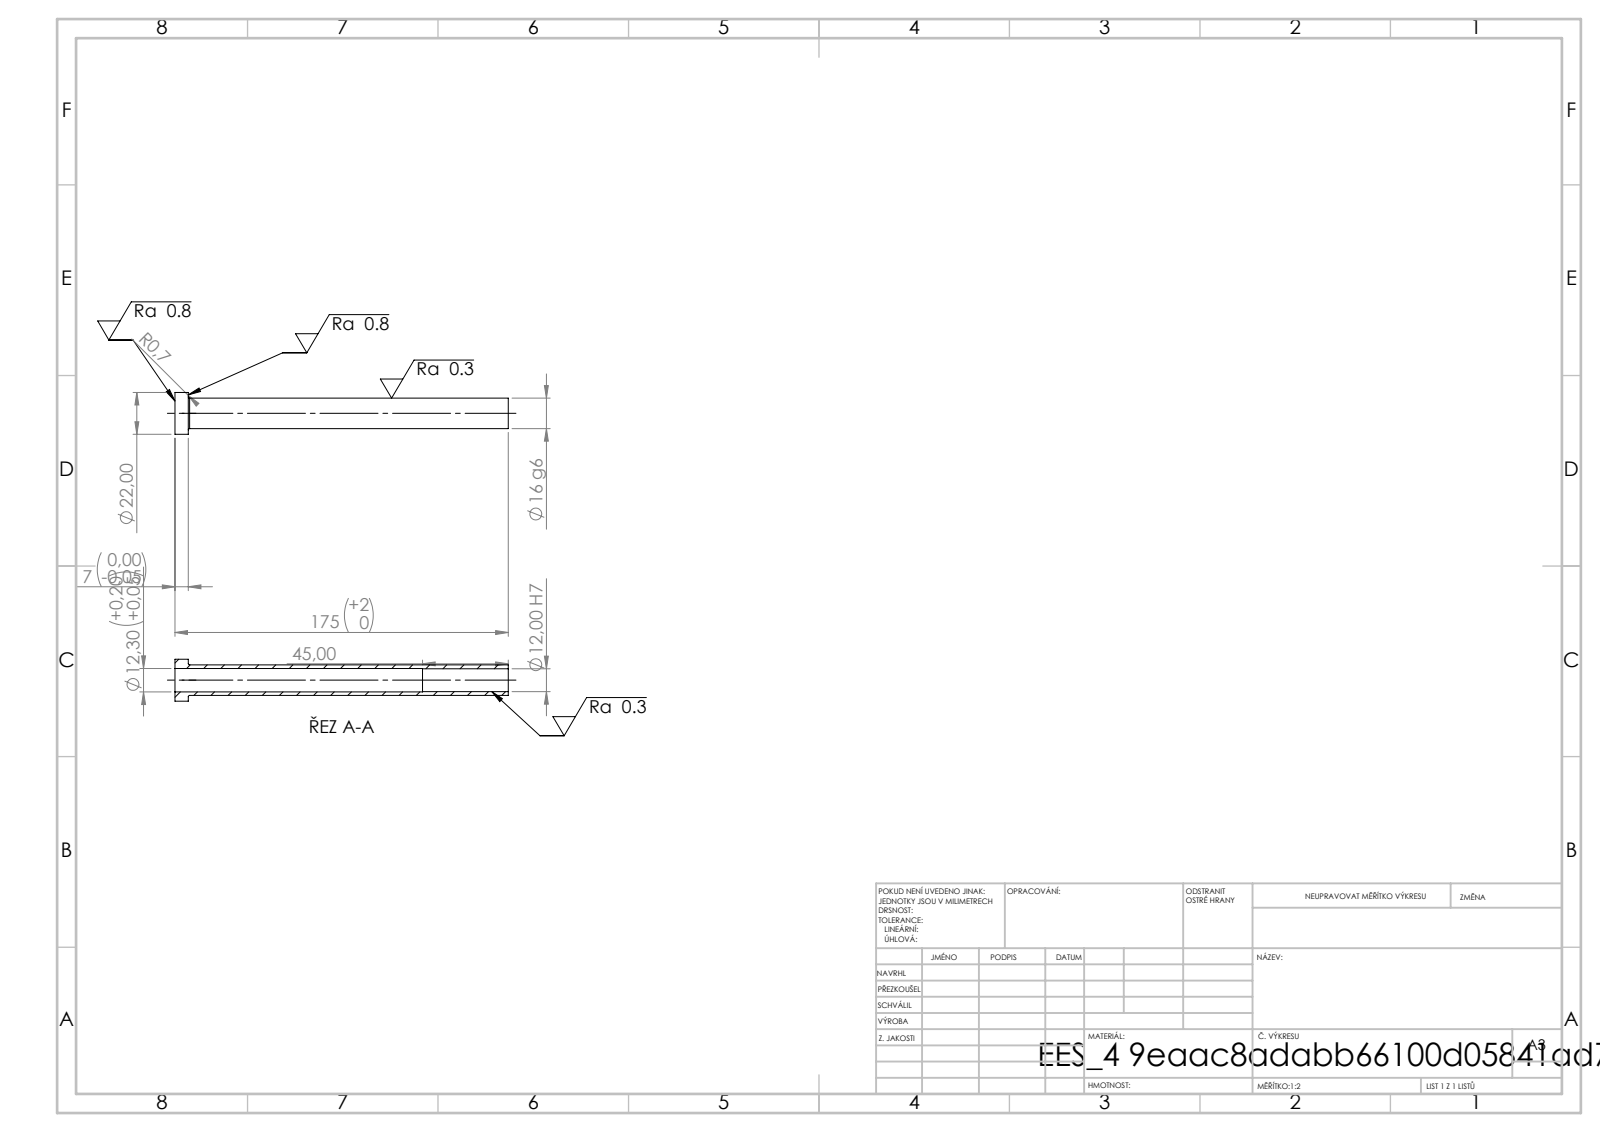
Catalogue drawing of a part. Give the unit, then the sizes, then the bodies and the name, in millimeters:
Units: millimetres
Overall size (bounding box): 175 × 22 × 22
Round holes (diameter × count): ⌀12 ×1, ⌀12.3 ×1
Round bosses / shafts (diameter × count): ⌀22 ×1, ⌀16 ×1
Main face-to-face distances: 7, 175, 168, 130, 123, 45
Volume: 15 908 mm³ · Surface area: 16 167 mm²
Bodies: 1 solid, 14 faces (4 planar, 8 cylindrical, 2 other)
STEP written by: SolidWorks 2019 (CONFIG_CONTROL_DESIGN)
